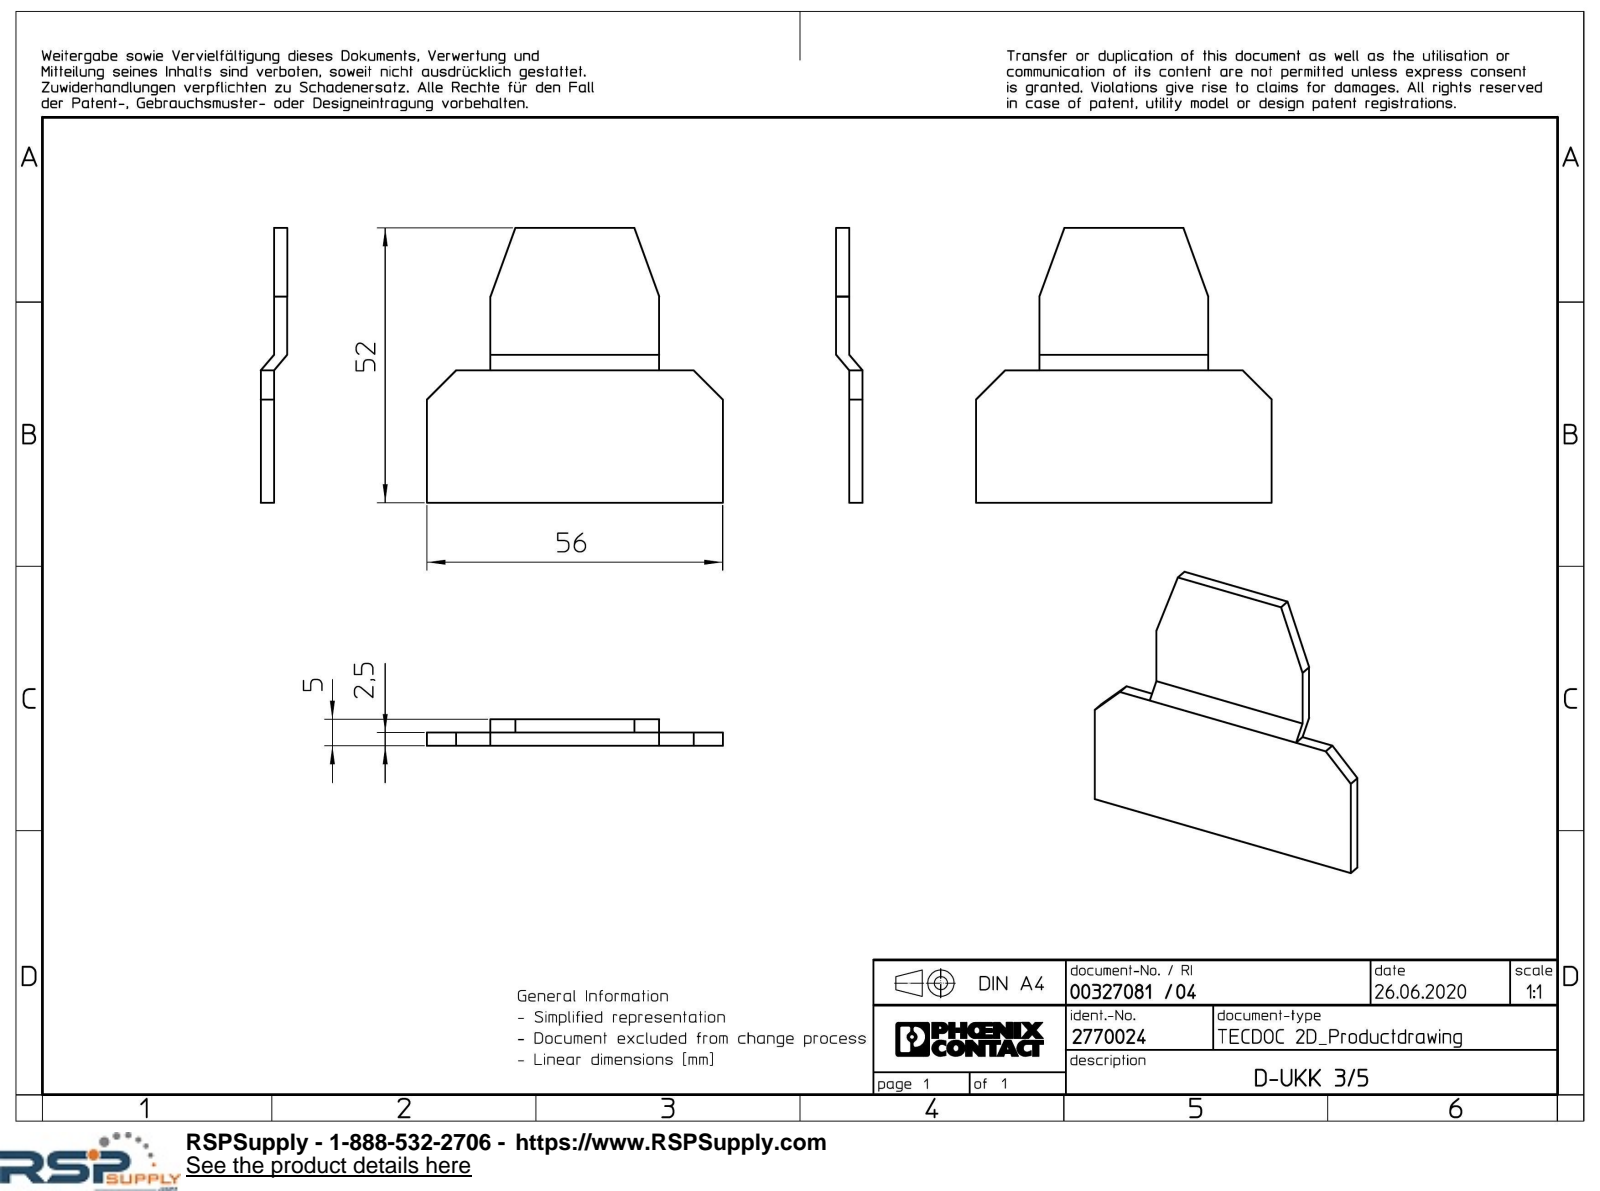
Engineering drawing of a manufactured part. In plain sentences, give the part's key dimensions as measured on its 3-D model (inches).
The part is named "D_UKK_3_5-select". Its 3-D file was written by "Creo Elements/Direct Modeling 20.1A 29-Sep-2018 (C) Parametric Technology GmbH (AUTOMOTIVE_DESIGN)". It is 1 solid with 18 faces: 18 planar, 0 cylindrical and 0 other. Overall it measures 2.205 by 2.047 by 0.197 inches. Its volume is 0.331 cubic inches and its surface area 7.606 square inches. The main face-to-face distances are 0.098, 0.197, 0.076, 0.472, 1.732, 2.047, 2.205, 1.26, 0.984, 1.063.
